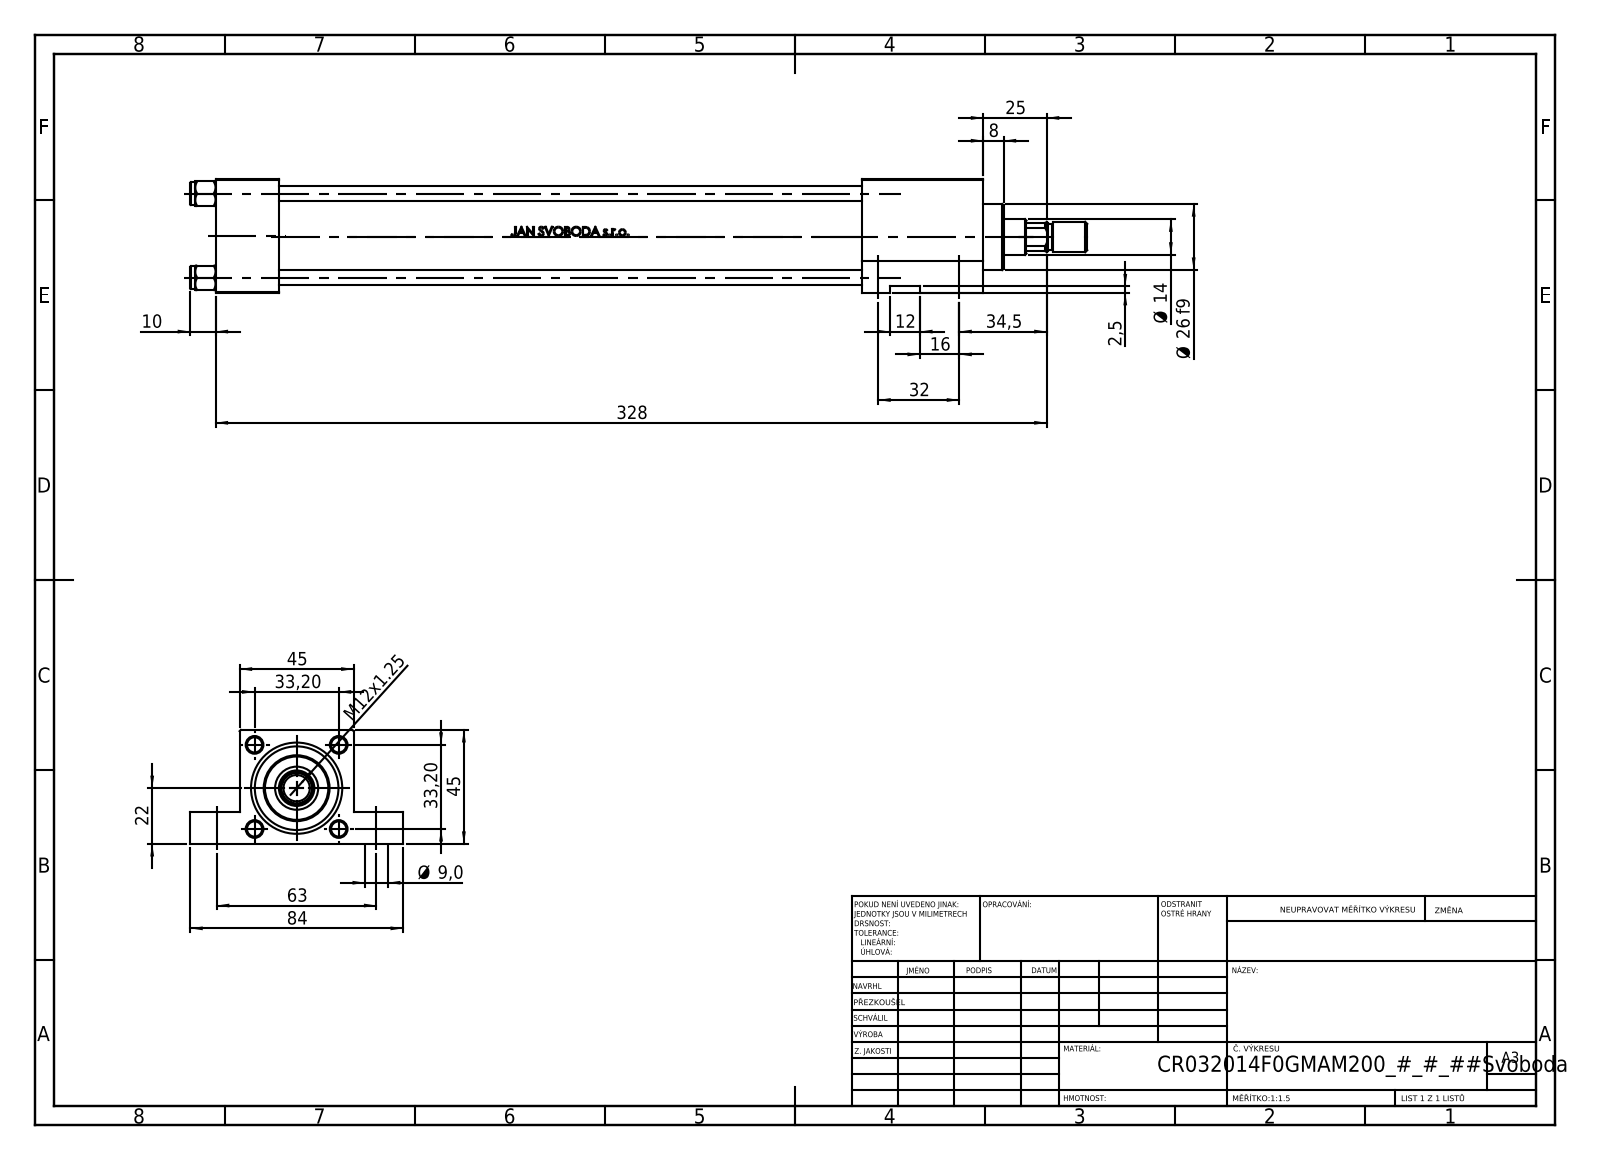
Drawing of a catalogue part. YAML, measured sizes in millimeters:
part_name: "V215CR_VCP_F; V215CR_F_Body; V215CR_F_TYCINKA; ROD_END_AH (+2 more)"
step_written_by: "SolidWorks 2019 (CONFIG_CONTROL_DESIGN)"
units: millimeters
bodies: {solids: 12, faces: 1116, planar: 440, cylindrical: 130, other: 546}
overall_size: [354, 84, 45]
volume: 321086
surface_area: 134636
round_holes:
  - {diameter: 6, count: 4}
  - {diameter: 9, count: 4}
  - {diameter: 7, count: 2}
  - {diameter: 20, count: 2}
  - {diameter: 6.5, count: 1}
  - {diameter: 13, count: 1}
  - {diameter: 13.16, count: 1}
  - {diameter: 14, count: 1}
  - {diameter: 17, count: 1}
  - {diameter: 24, count: 1}
  - {diameter: 32, count: 1}
  - {diameter: 33, count: 1}
round_bosses_or_shafts:
  - {diameter: 9, count: 4}
  - {diameter: 38, count: 1}
  - {diameter: 26, count: 1}
  - {diameter: 12, count: 1}
  - {diameter: 10, count: 1}
partial_cylinders:
  - {radius: 6.5, count: 1}
face_to_face_distances: [45, 25, 278, 303, 32.5, 255, 230, 48, 12.5, 10]
hole_center_spacings: [33.2, 23.13, 23.83, 32, 46.95, 63, 70.66, 255.5]
